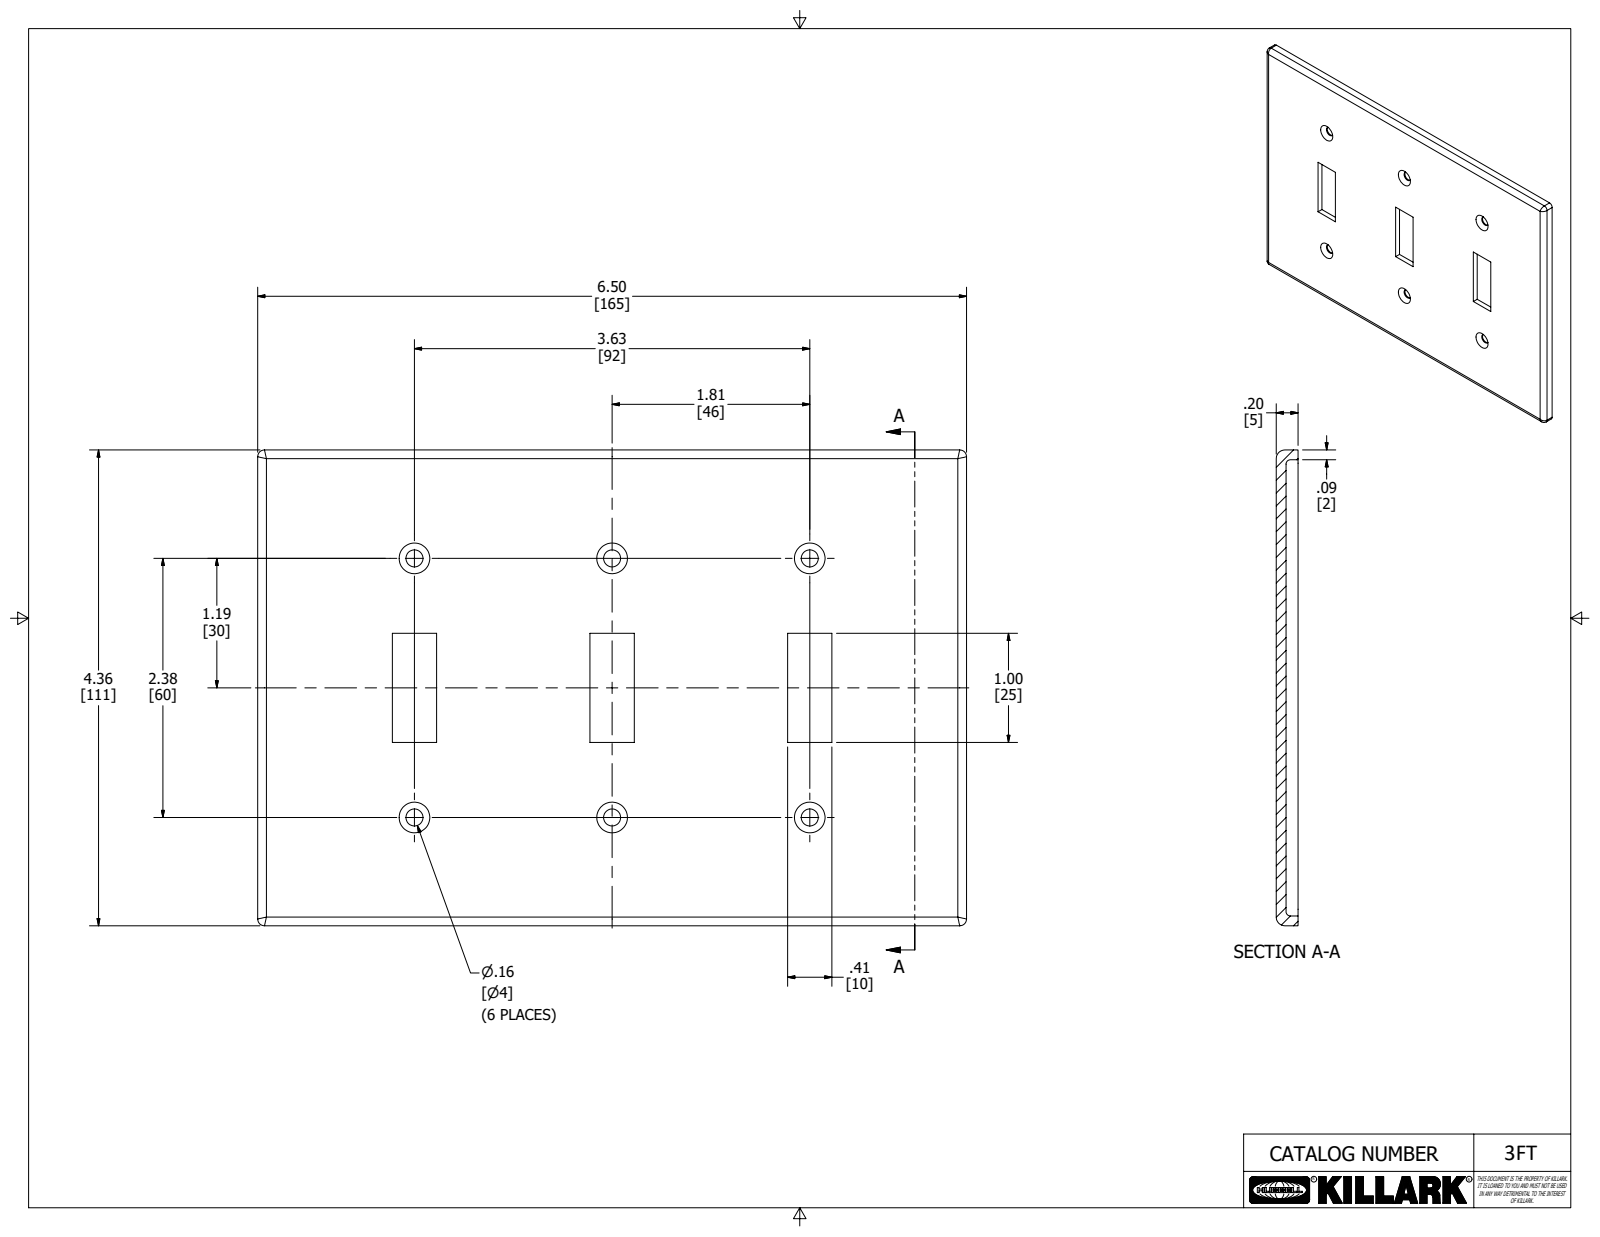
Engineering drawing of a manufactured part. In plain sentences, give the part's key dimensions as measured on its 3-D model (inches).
The part is named "07806-3". Its 3-D file was written by "Autodesk Inventor 2020 (AUTOMOTIVE_DESIGN)". It is 1 solid with 59 faces: 23 planar, 22 cylindrical and 14 other. Overall it measures 6.5 by 4.362 by 0.2 inches. Its volume is 2.612 cubic inches and its surface area 60.5 square inches. Round holes: 6 of diameter 0.156. Partial cylindrical surfaces (rounded edges, fillets, slot ends): 6 of radius 0.062, 4 of radius 0.04, 4 of radius 0.08, 2 of radius 0.031. The main face-to-face distances are 0.09, 0.11, 0.2, 4.272, 4.362, 6.41, 6.5, 4.182, 6.32, 1.681. The hole center spacings are 1.813, 2.988, 2.375, 3.625, 4.334.
